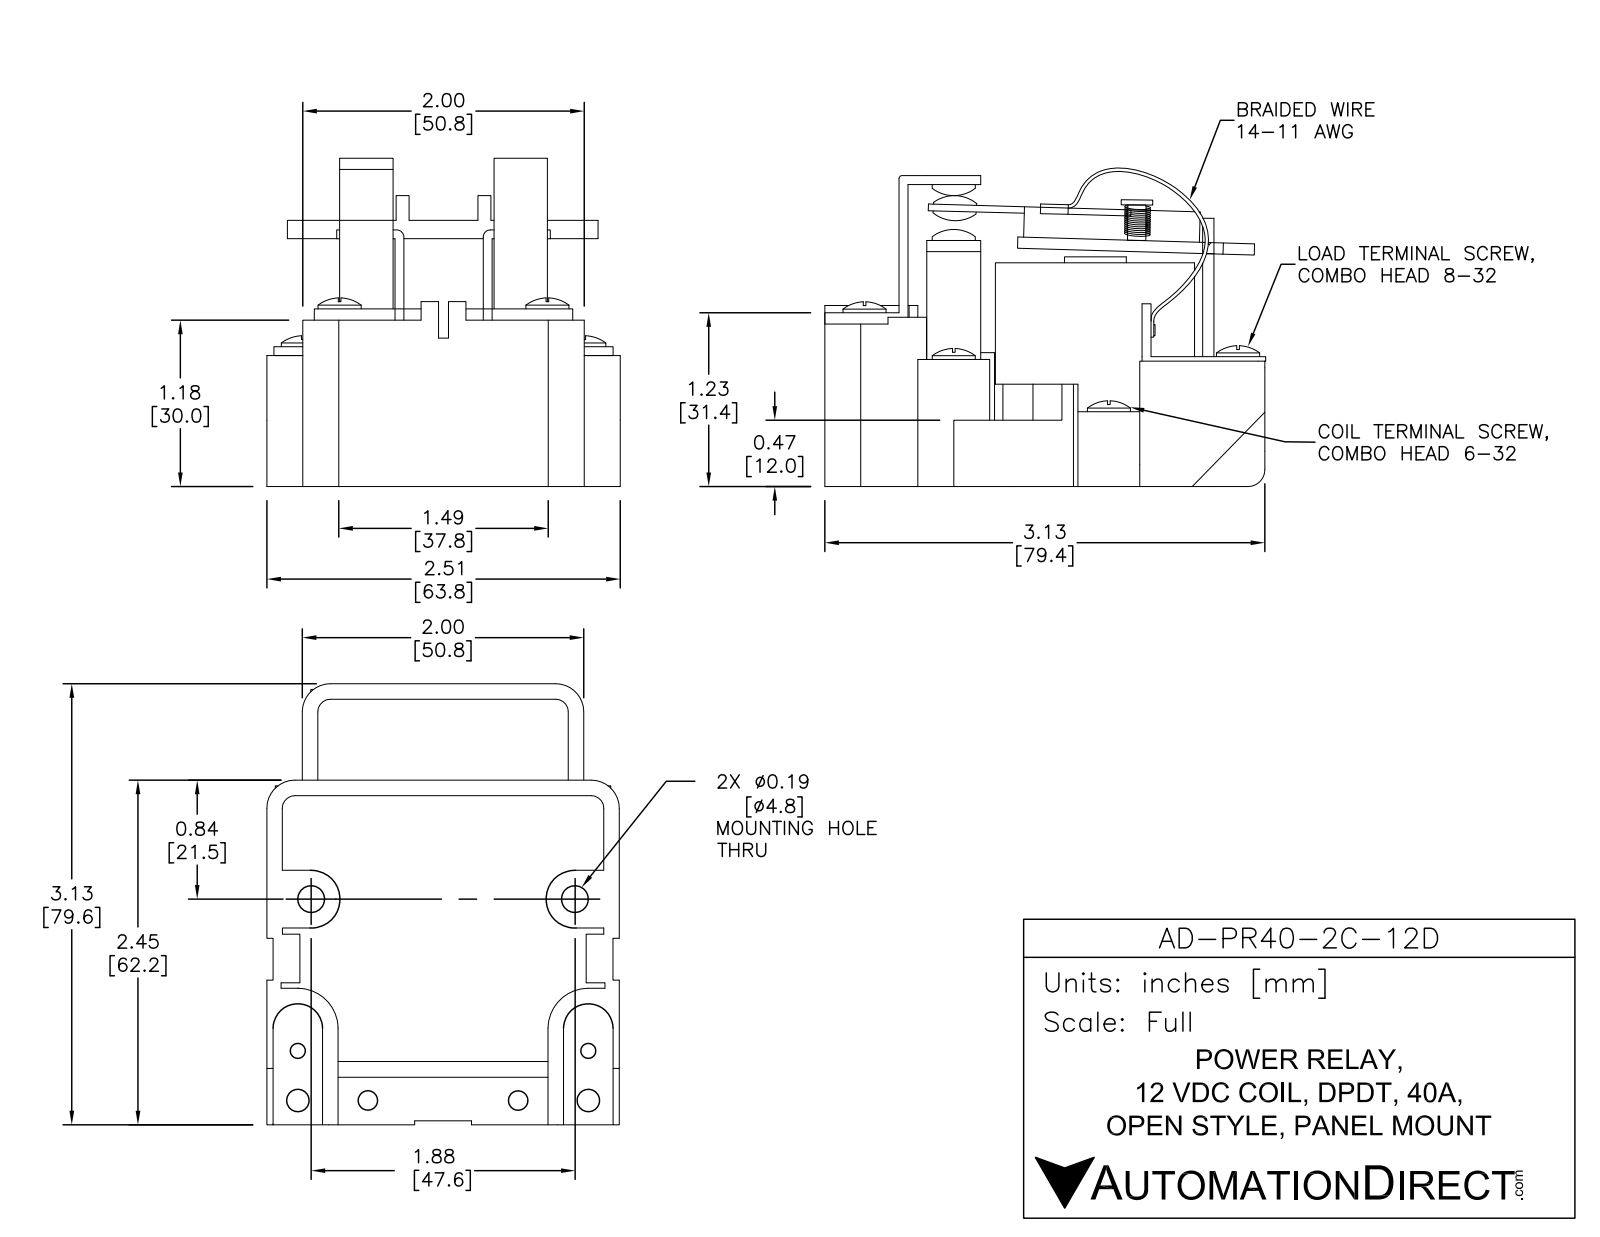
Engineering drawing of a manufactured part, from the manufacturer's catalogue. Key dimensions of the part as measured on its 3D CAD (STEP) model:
Part name (STEP PRODUCT): AD-PR40-2C-12D
STEP written by: SolidWorks 2013 (AUTOMOTIVE_DESIGN)
Units: millimetres
Bodies: 37 solids, 859 faces (564 planar, 185 cylindrical, 110 other)
Overall size (bounding box): 83.31 × 64.94 × 55.05
Volume: 127 413 mm³ · Surface area: 42 988 mm²
Round holes (diameter × count): ⌀5 ×4, ⌀3.33 ×2, ⌀10 ×2, ⌀30 ×1
Round bosses / shafts (diameter × count): ⌀7.75 ×6, ⌀6.5 ×6, ⌀5.28 ×4, ⌀6.85 ×2, ⌀5.5 ×2, ⌀3.5 ×2, ⌀35.5 ×1, ⌀18 ×1
Partial cylindrical surfaces — rounded edges, fillets, slot ends (radius × count): R1 ×15, R0.75 ×10, R3 ×5, R5 ×5, R0.38 ×4, R1.48 ×4, R1.5 ×4, R7 ×4
Main face-to-face distances: 2, 1.5, 1, 10, 6.5, 4.5, 36.25, 12, 48.25, 3.5
Hole centre spacings: 10, 26.2, 27.51, 29.92, 36.54, 37.51, 49.24, 50.25
